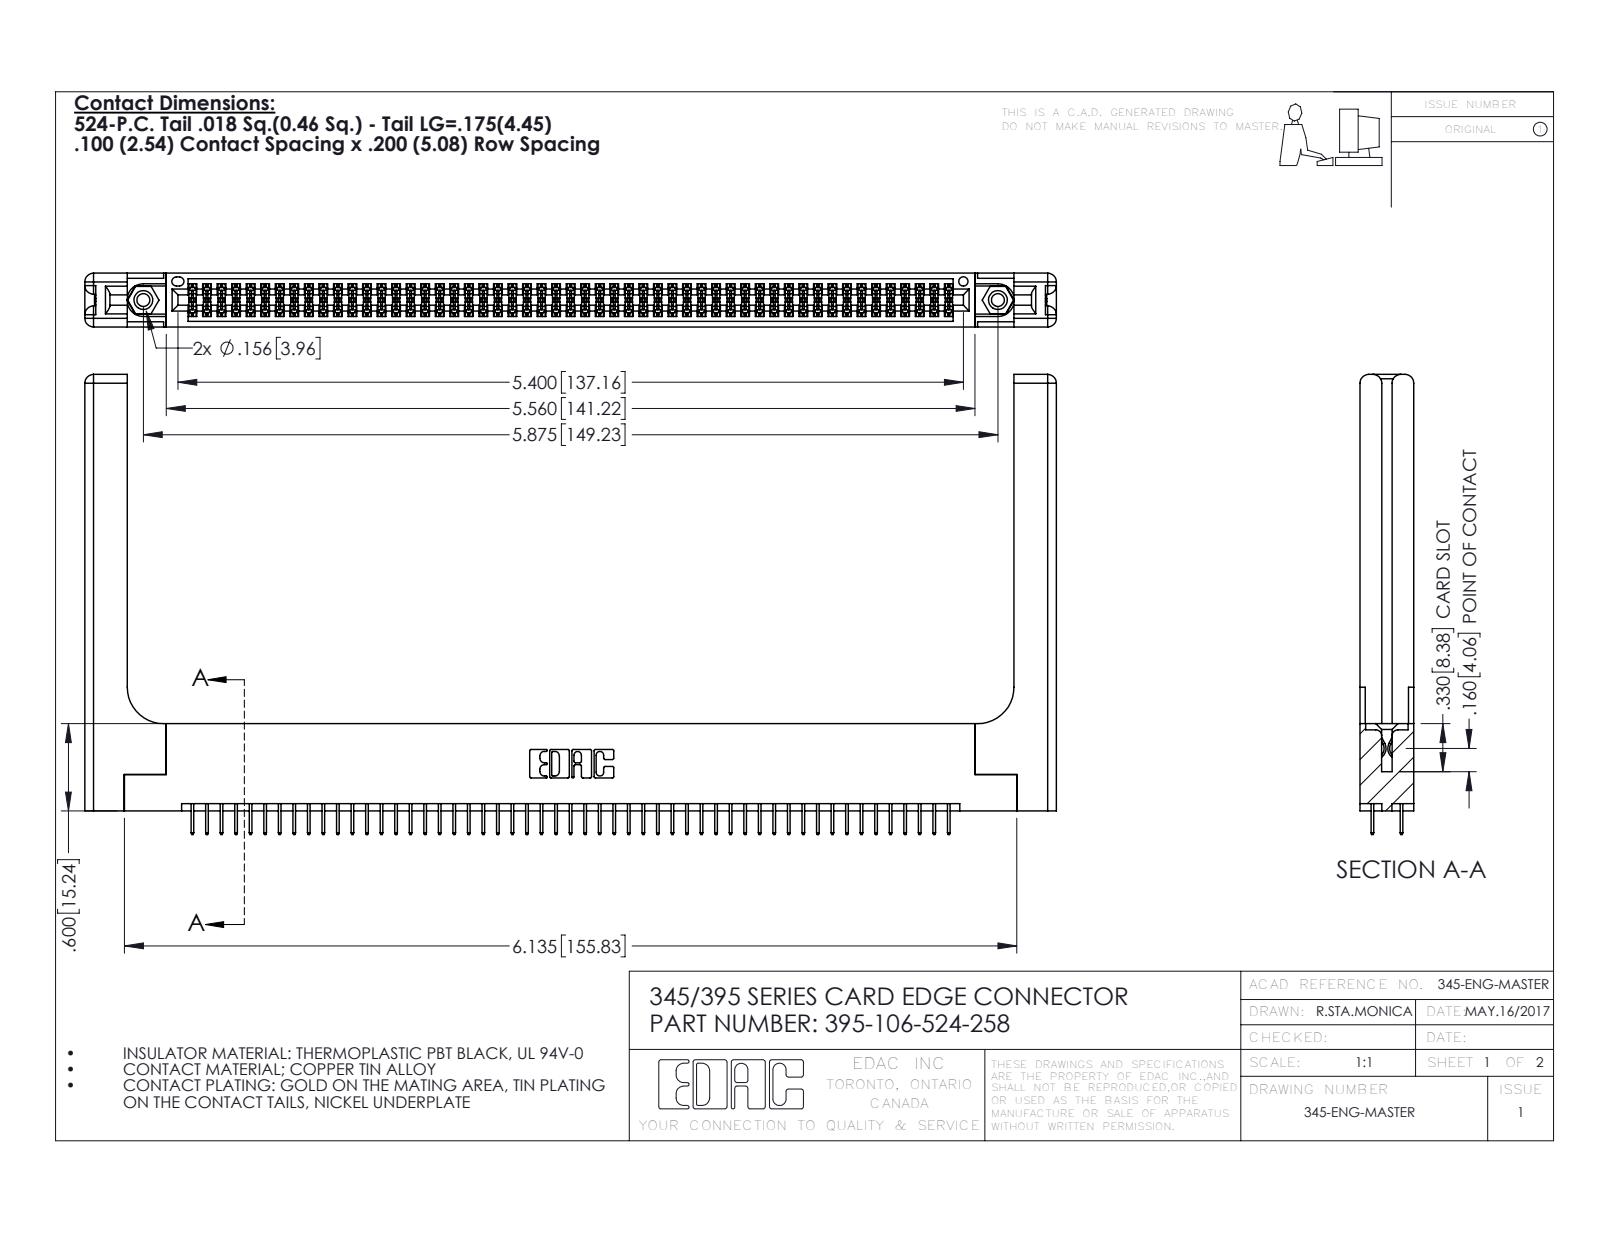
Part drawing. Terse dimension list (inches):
name: 345 Part_Flush Mounting Lugs - 0.156 Dia-TH; 345-292-001_345-293-124; 395-106-524-258; 345-250-001_345-250-001-102 (+1 more)
written by: SolidWorks 2016 (CONFIG_CONTROL_DESIGN)
unit: in
bodies: 111 solids, 6106 faces (4362 planar, 1684 cylindrical, 60 other)
size: 6.679 × 3.162 × 0.37
volume: 1.519 in³; area: 45.14 in²
holes: 2× ⌀0.089, 2× ⌀0.125, 2× ⌀0.156, 1× ⌀0.064
bosses: 2× ⌀0.155
rounds: 159× R0.006, 22× R0.01, 16× R0.06, 6× R0.007, 6× R0.031, 3× R0.026, 2× R0.014, 2× R0.019
face distances: 0.072, 0.37, 0.298, 0.2, 0.098, 0.272, 0.025, 0.225, 0.148, 0.15
hole spacings: 0.27, 5.639, 5.875
